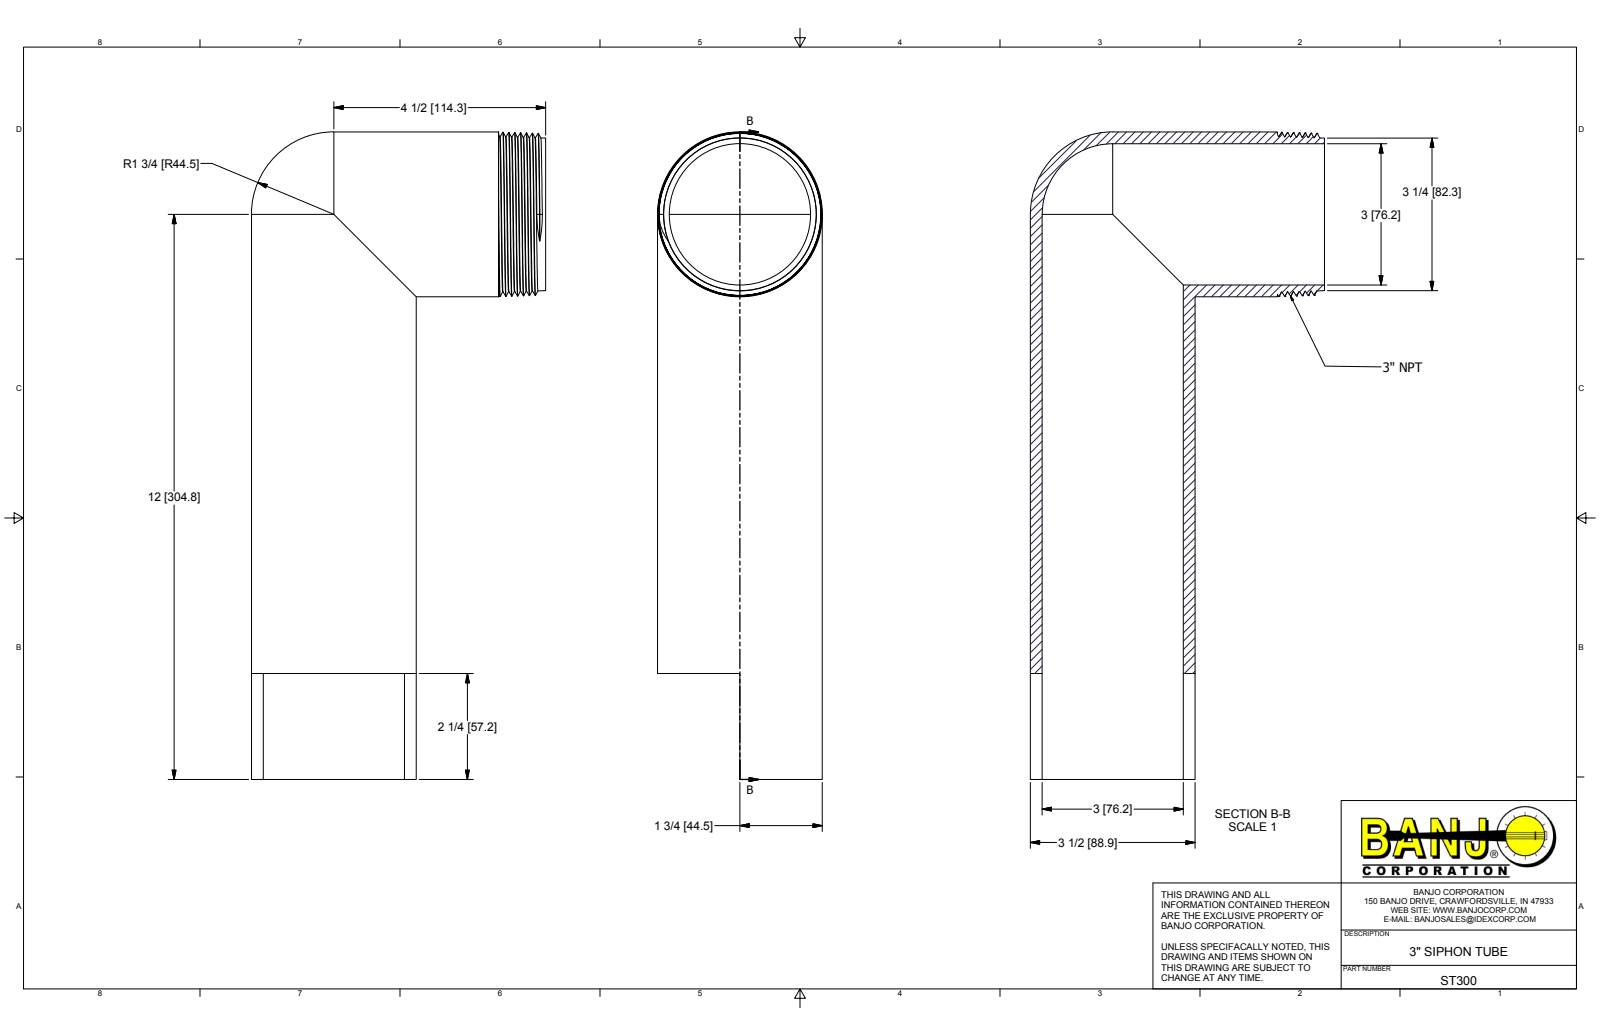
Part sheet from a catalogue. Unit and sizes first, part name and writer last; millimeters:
Units: millimetres
Overall size (bounding box): 349.25 × 158.75 × 88.9
Round holes (diameter × count): ⌀76.2 ×2
Round bosses / shafts (diameter × count): ⌀88.9 ×2
Partial cylindrical surfaces — rounded edges, fillets, slot ends (radius × count): R23.07 ×1
Main face-to-face distances: 57.15
Volume: 620 862 mm³ · Surface area: 208 051 mm²
Bodies: 1 solid, 26 faces (5 planar, 5 cylindrical, 16 other)
Part name (STEP PRODUCT): ST300
STEP written by: Autodesk Inventor 2016 (AUTOMOTIVE_DESIGN)
